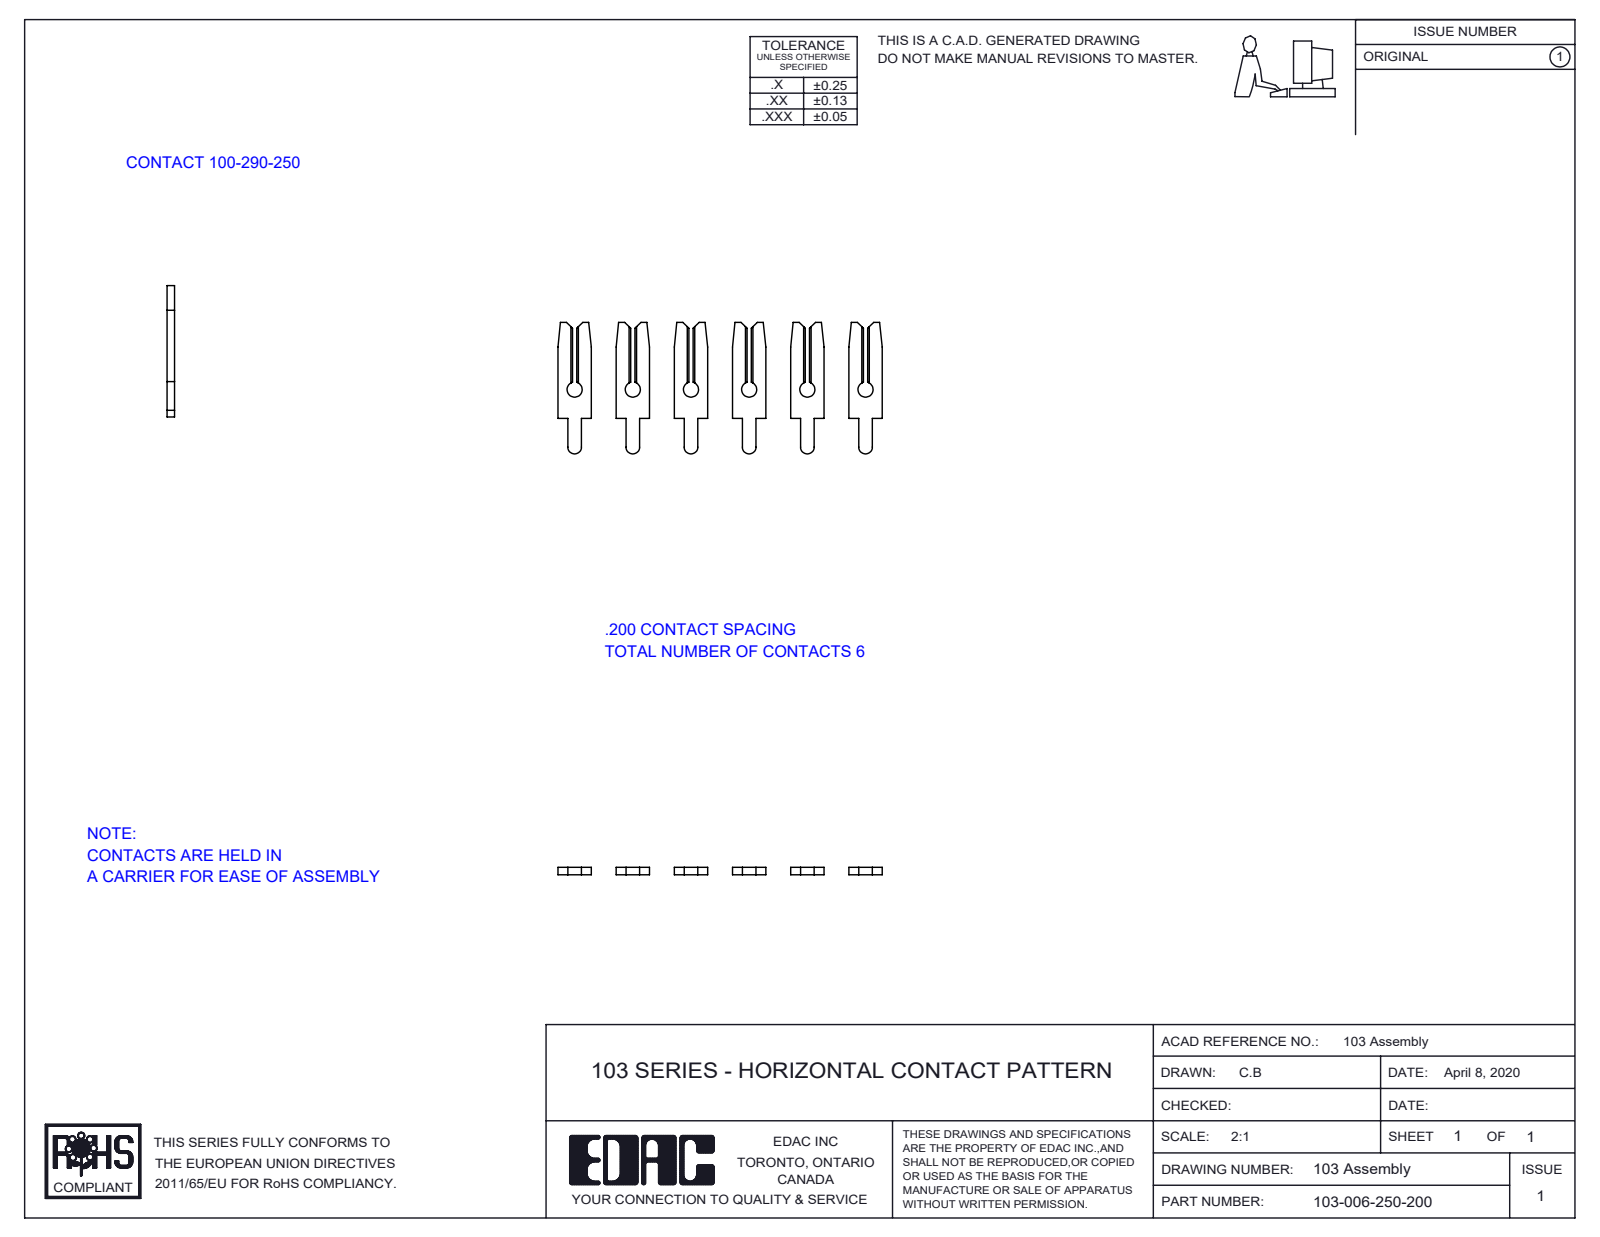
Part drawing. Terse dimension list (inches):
name: 100-290-001_100-290-250; 103-006-250-200
written by: SolidWorks 2016 (CONFIG_CONTROL_DESIGN)
unit: in
bodies: 6 solids, 144 faces (120 planar, 24 cylindrical, 0 other)
size: 1.115 × 0.452 × 0.026
volume: 0.006 in³; area: 0.682 in²
holes: 6× ⌀0.052
rounds: 6× R0.024
face distances: 0.026, 0.2, 0.4, 0.6, 0.115, 0.141, 0.315, 0.085, 0.8, 0.283
hole spacings: 0.2, 0.4, 0.6, 0.8, 1
